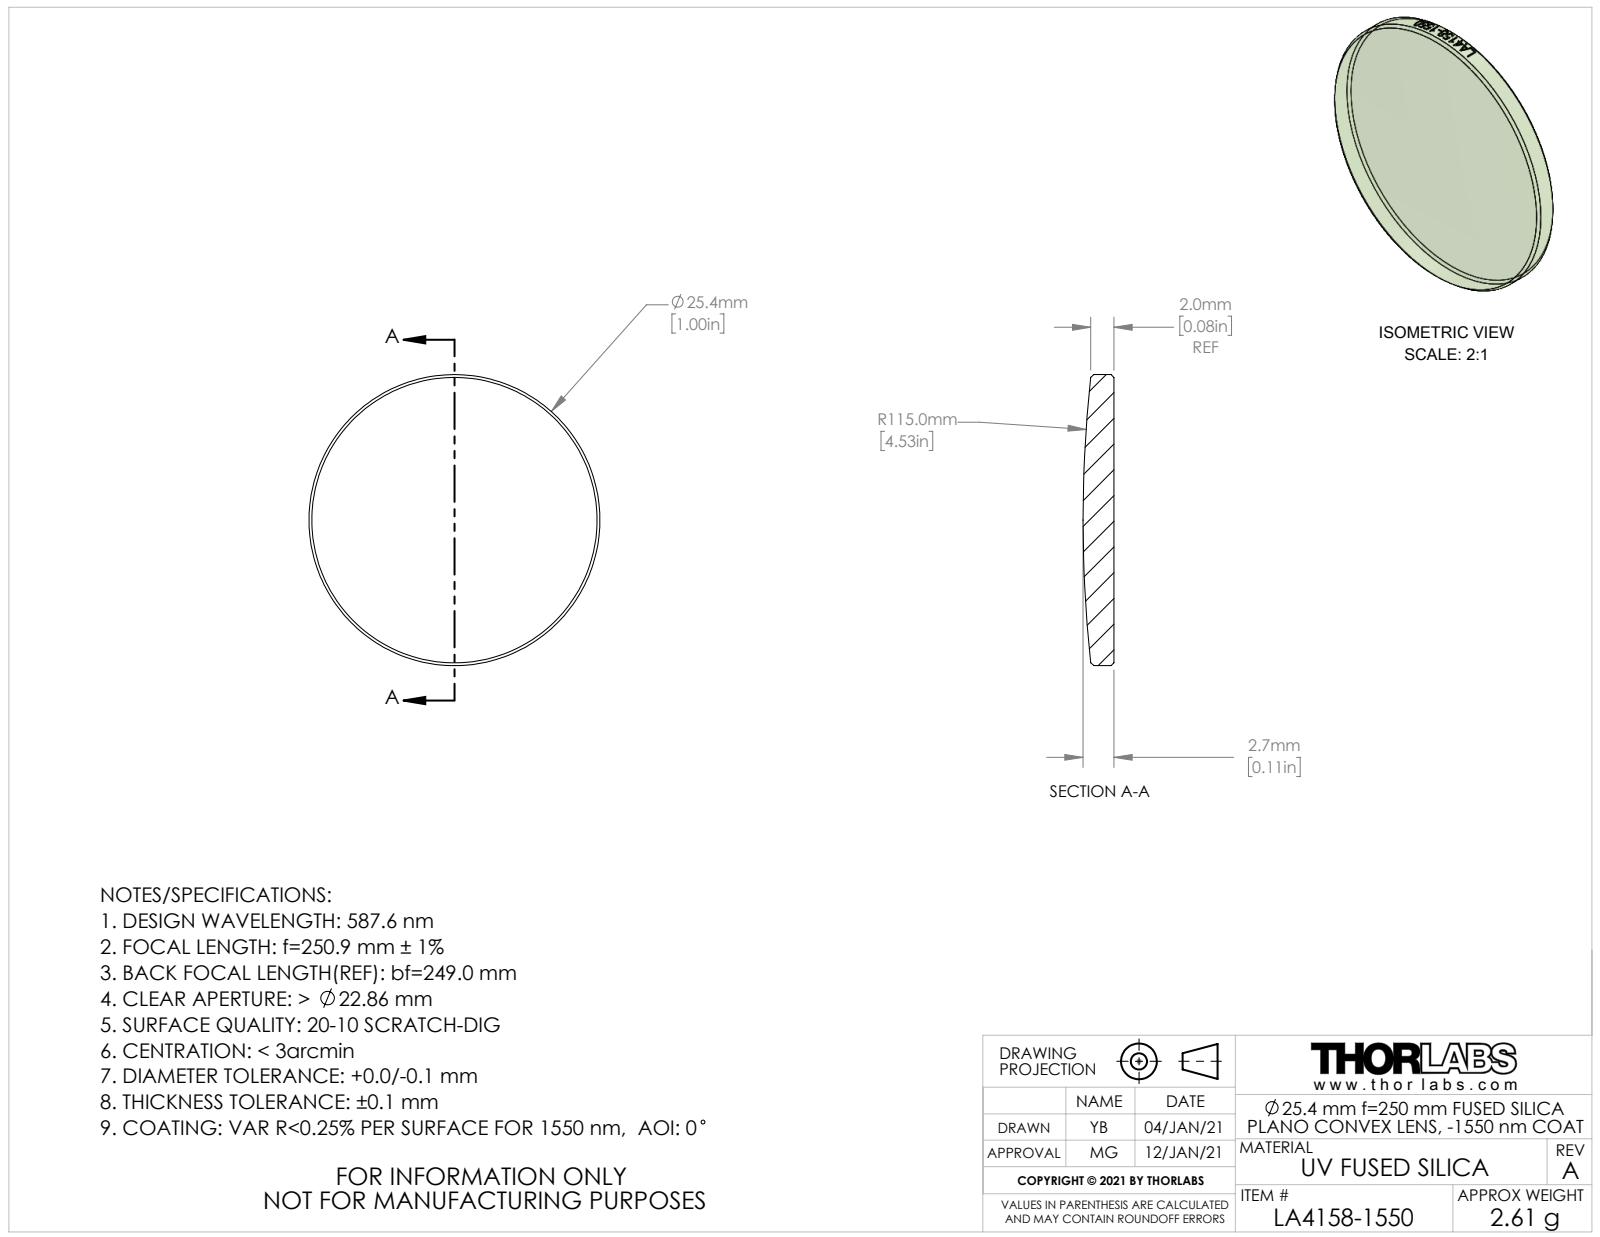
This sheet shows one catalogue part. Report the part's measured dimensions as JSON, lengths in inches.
{"part_name": "CTN015954-E0W", "step_written_by": "SolidWorks 2018 (AUTOMOTIVE_DESIGN)", "units": "inches", "bodies": {"solids": 1, "faces": 28, "planar": 1, "cylindrical": 21, "other": 6}, "overall_size": [1, 1, 0.106], "volume_in3": 0.072, "surface_area_in2": 1.786, "round_bosses_or_shafts": [[1, 1]]}
